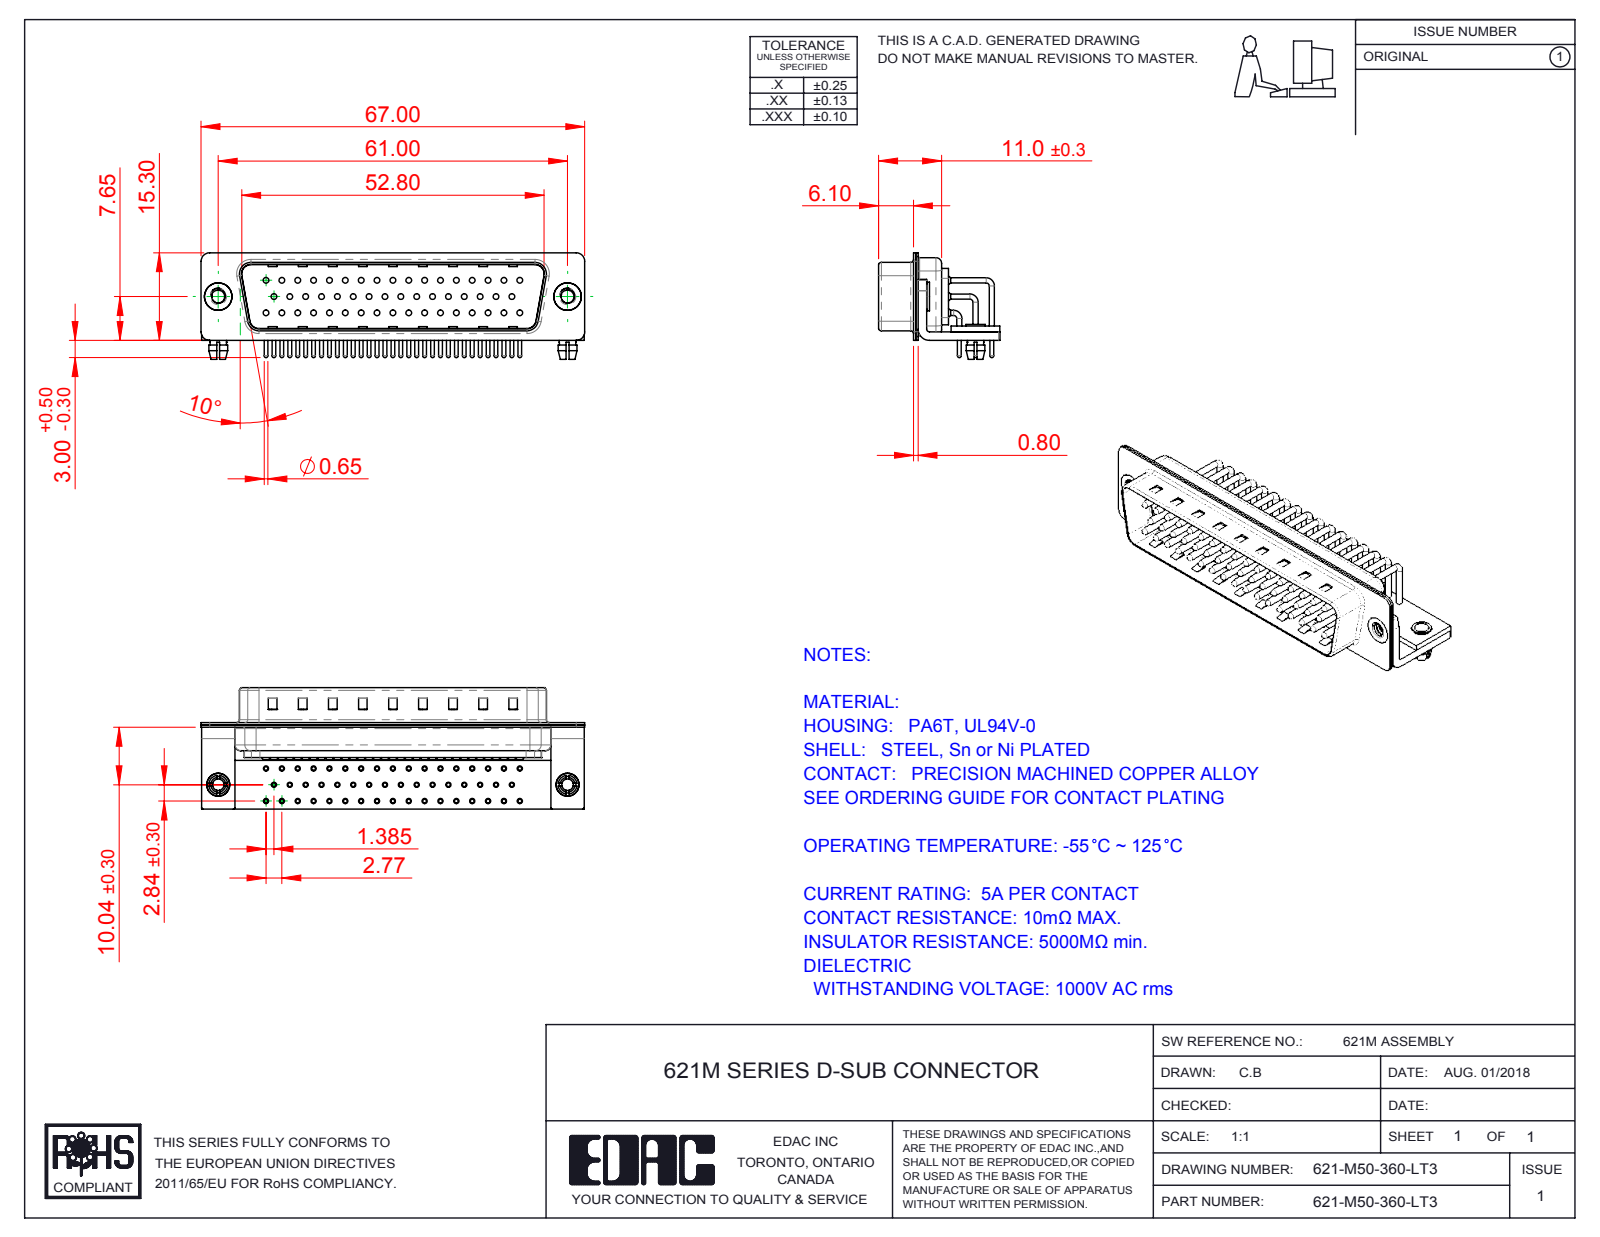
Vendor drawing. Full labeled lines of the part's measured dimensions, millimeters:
Part name (STEP PRODUCT): 621M Stabilizer Board_50 Contacts; 621M Shell Rear_50 Contacts; 621M Stabilizer Bracket_50 Contacts; 621M Contact Row 1_50 Contacts (+7 more)
STEP written by: SolidWorks 2016 (CONFIG_CONTROL_DESIGN)
Units: millimetres
Bodies: 60 solids, 6154 faces (3477 planar, 2095 cylindrical, 582 other)
Overall size (bounding box): 67 × 21.2 × 18.6
Volume: 5 779 mm³ · Surface area: 14 799 mm²
Round holes (diameter × count): ⌀2 ×52, ⌀0.9 ×50, ⌀1 ×50, ⌀1.7 ×50, ⌀2.26 ×2, ⌀2.5 ×2, ⌀3.2 ×2, ⌀4 ×2, ⌀4.8 ×2
Round bosses / shafts (diameter × count): ⌀0.9 ×58, ⌀1.5 ×50, ⌀0.65 ×50, ⌀5 ×2, ⌀4.9 ×2, ⌀4 ×2, ⌀3.4 ×2, ⌀3.3 ×2
Partial cylindrical surfaces — rounded edges, fillets, slot ends (radius × count): R1.01 ×50, R0.25 ×16, R1.5 ×16, R2 ×13, R0.5 ×9, R1.6 ×8, R0.6 ×4, R0.65 ×4
Main face-to-face distances: 0.4, 1, 11.55, 0.83, 1.5, 5.7, 0.43, 11.95, 6.1, 11.72
Hole centre spacings: 2.77, 3.16, 5.54, 8.31, 11.08, 13.85, 16.62, 19.39
